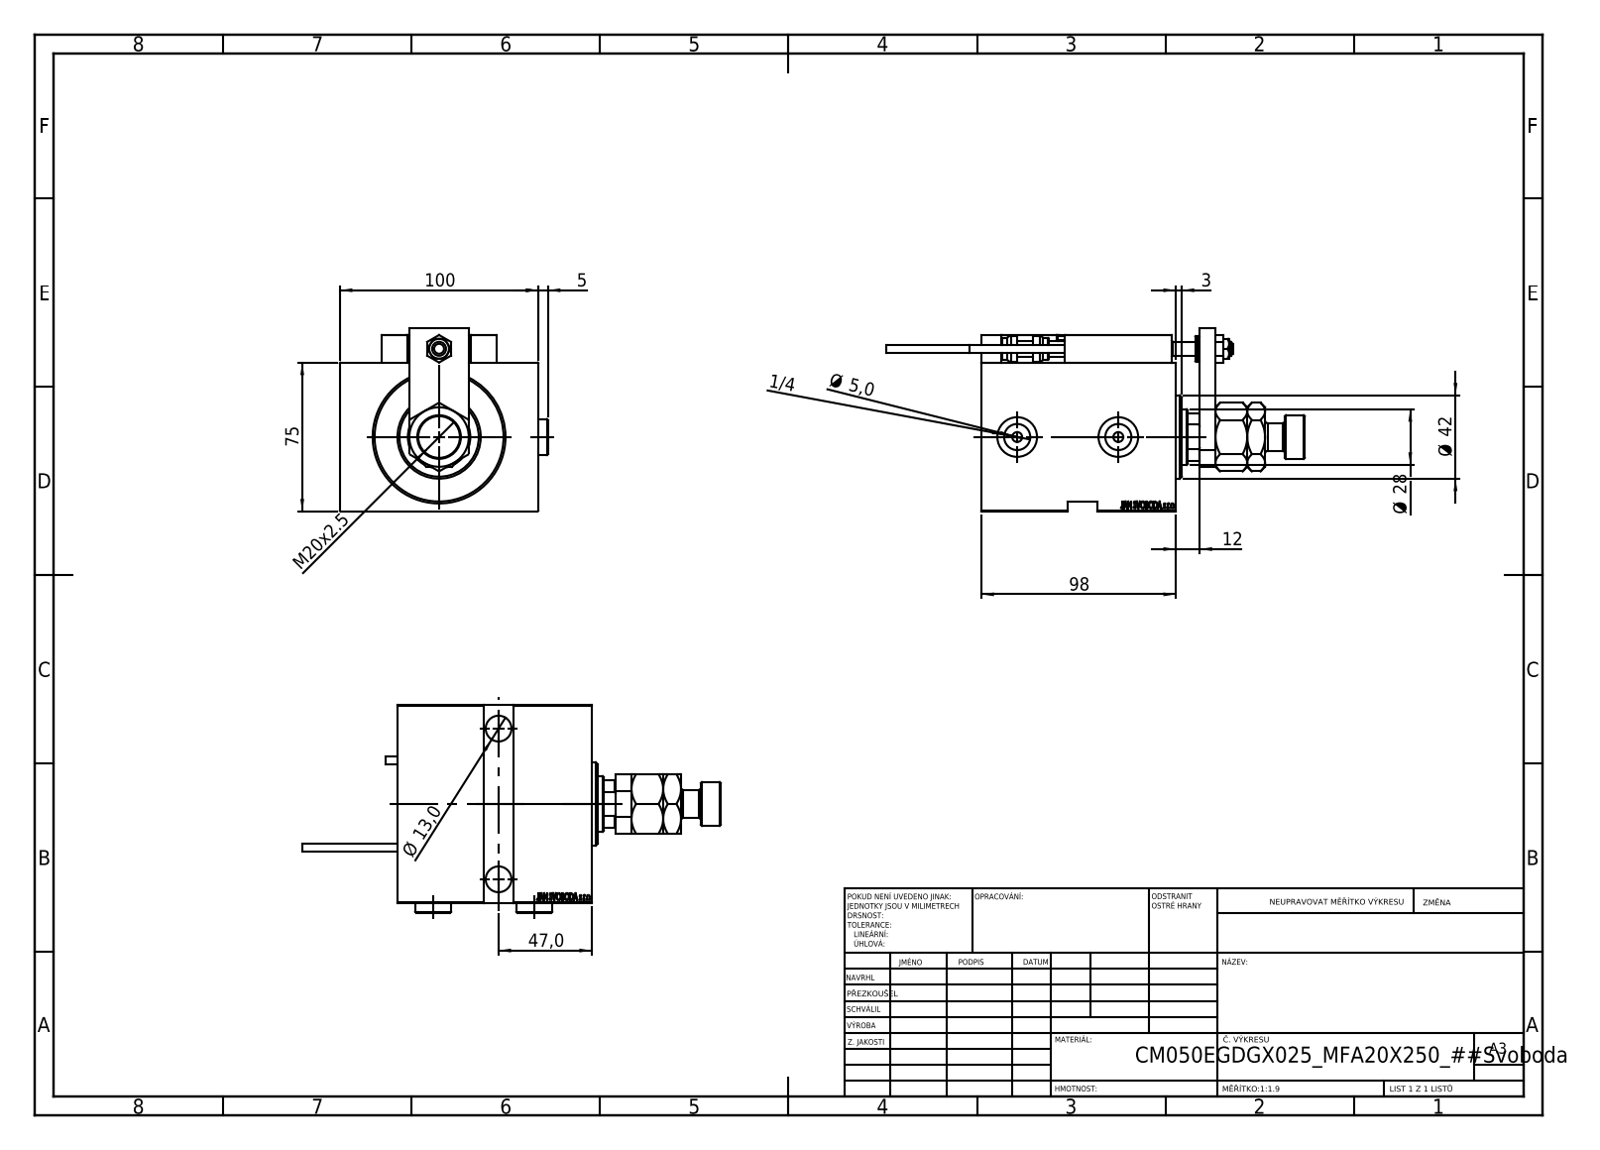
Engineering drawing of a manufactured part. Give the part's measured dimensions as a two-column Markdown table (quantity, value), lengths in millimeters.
| quantity | value |
| --- | --- |
| part name | SWITCH DIM B,W; Zatka_OIL_PORT; MAGNET; V450CM_E_Body (+7 more) |
| STEP written by | SolidWorks 2019 (CONFIG_CONTROL_DESIGN) |
| units | millimeters |
| bodies | 27 solids, 1391 faces (620 planar, 194 cylindrical, 577 other) |
| overall size | 211 × 104.9 × 92.5 |
| volume | 752 715 mm³ |
| surface area | 133 923 mm² |
| round holes (diameter × count) | 8 × 5, 3.2 × 4, 4 × 4, 5 × 4, 20 × 3, 13 × 2, 13.16 × 2, 19 × 2, 7 × 1, 18.5 × 1, 28 × 1, 31.5 × 1 |
| round bosses / shafts (diameter × count) | 18 × 2, 5 × 2, 3.8 × 2, 52 × 1, 42 × 1, 22 × 1, 14 × 1, 13 × 1 |
| partial cylindrical surfaces (radius × count) | 0.3 × 30, 3 × 2, 13.5 × 1 |
| main face-to-face distances | 75, 14, 100, 98, 84, 5, 25, 79, 20, 32 |
| hole center spacings | 11.37, 20, 29.59, 29.69, 36.06, 42.19, 48.83, 50.04 |
